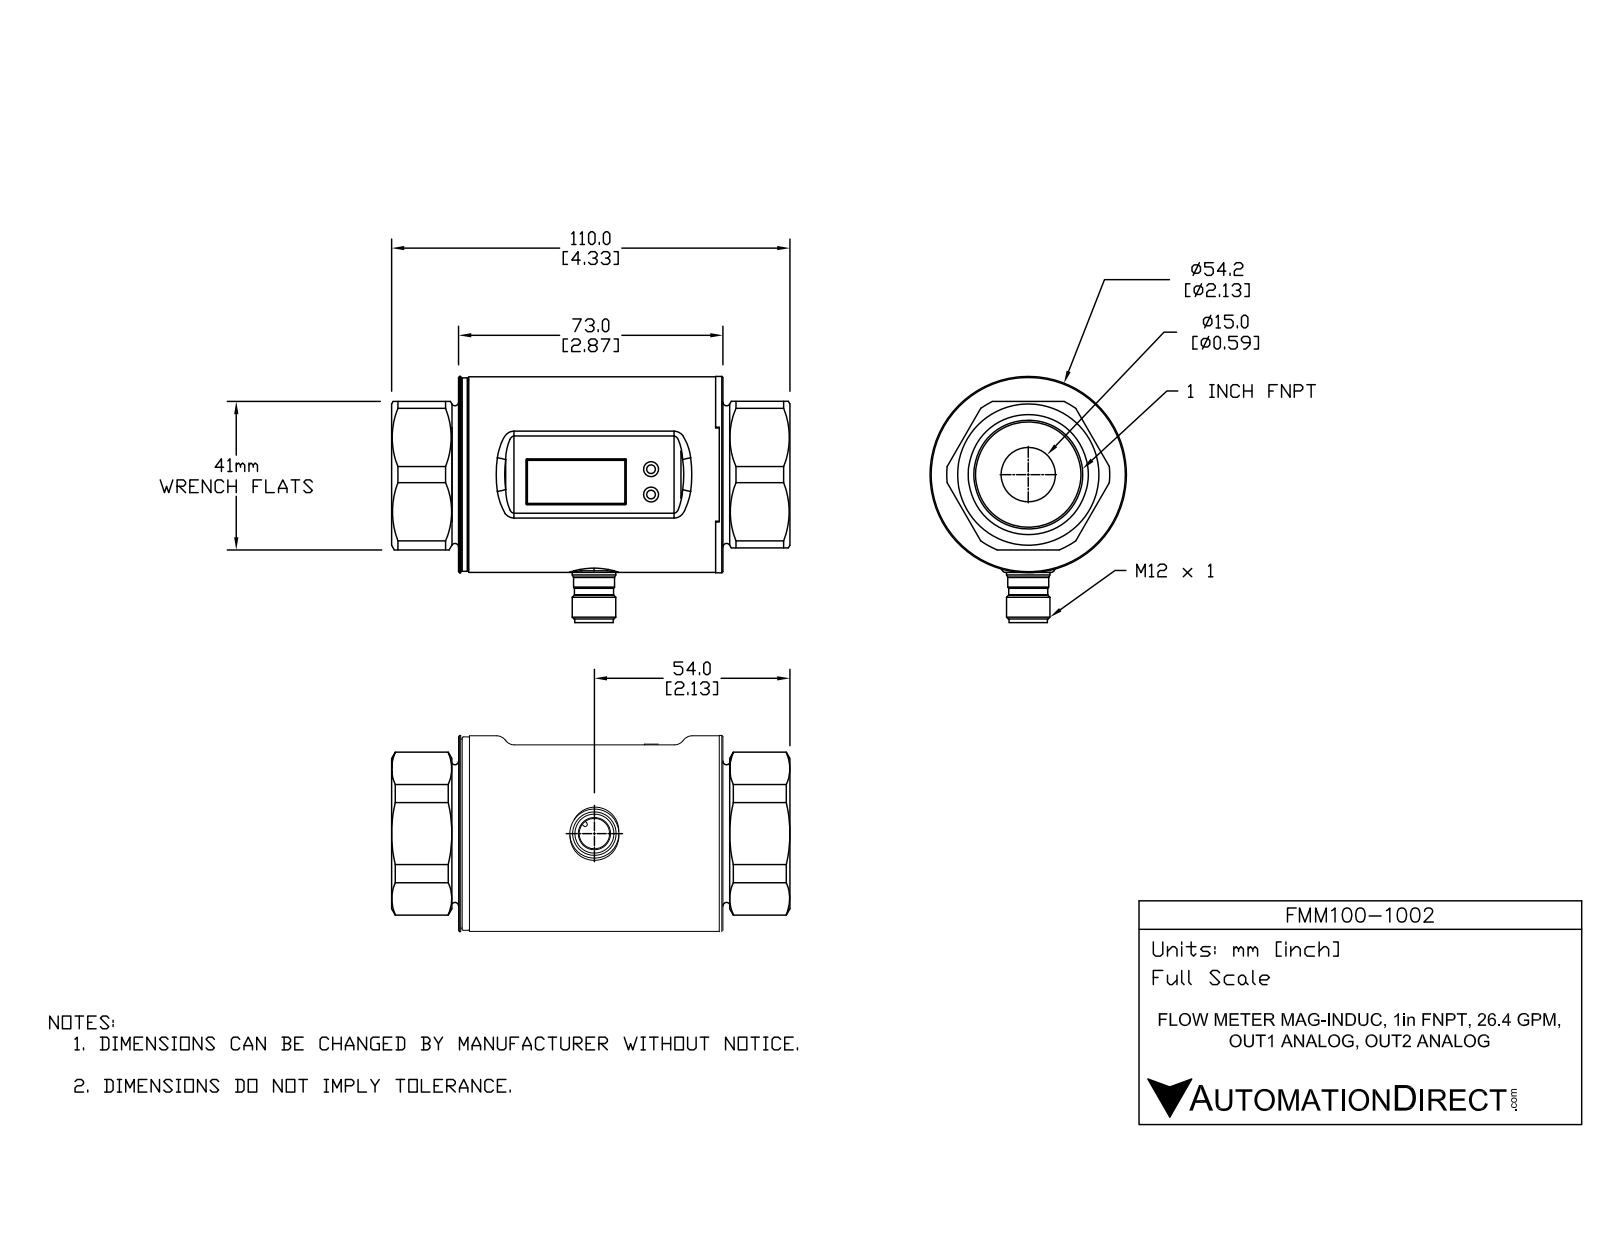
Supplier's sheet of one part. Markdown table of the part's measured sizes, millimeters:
| quantity | value |
| --- | --- |
| part name | FMM100-1002 |
| STEP written by | SolidWorks 2015 (AUTOMOTIVE_DESIGN) |
| units | millimeters |
| bodies | 11 solids, 214 faces (84 planar, 85 cylindrical, 45 other) |
| overall size | 109.99 × 67.85 × 54.2 |
| volume | 62 314 mm³ |
| surface area | 62 669 mm² |
| round holes (diameter × count) | 1.5 × 2, 3.6 × 2, 4.11 × 2, 8.4 × 1, 12 × 1, 15 × 1, 30 × 1, 52 × 1 |
| round bosses / shafts (diameter × count) | 3.9 × 2, 54.2 × 1, 54 × 1, 53.4 × 1, 52.2 × 1, 40 × 1, 12 × 1, 11.3 × 1 |
| partial cylindrical surfaces (radius × count) | 1 × 4, 0.3 × 2, 2 × 2, 3 × 2, 0.6 × 1, 22.5 × 1 |
| main face-to-face distances | 70, 2, 1, 5, 68, 71.7, 72, 72.7, 73, 1.87 |
| hole center spacings | 13, 1.25, 7, 8, 9.25, 21, 22.25, 26 |
